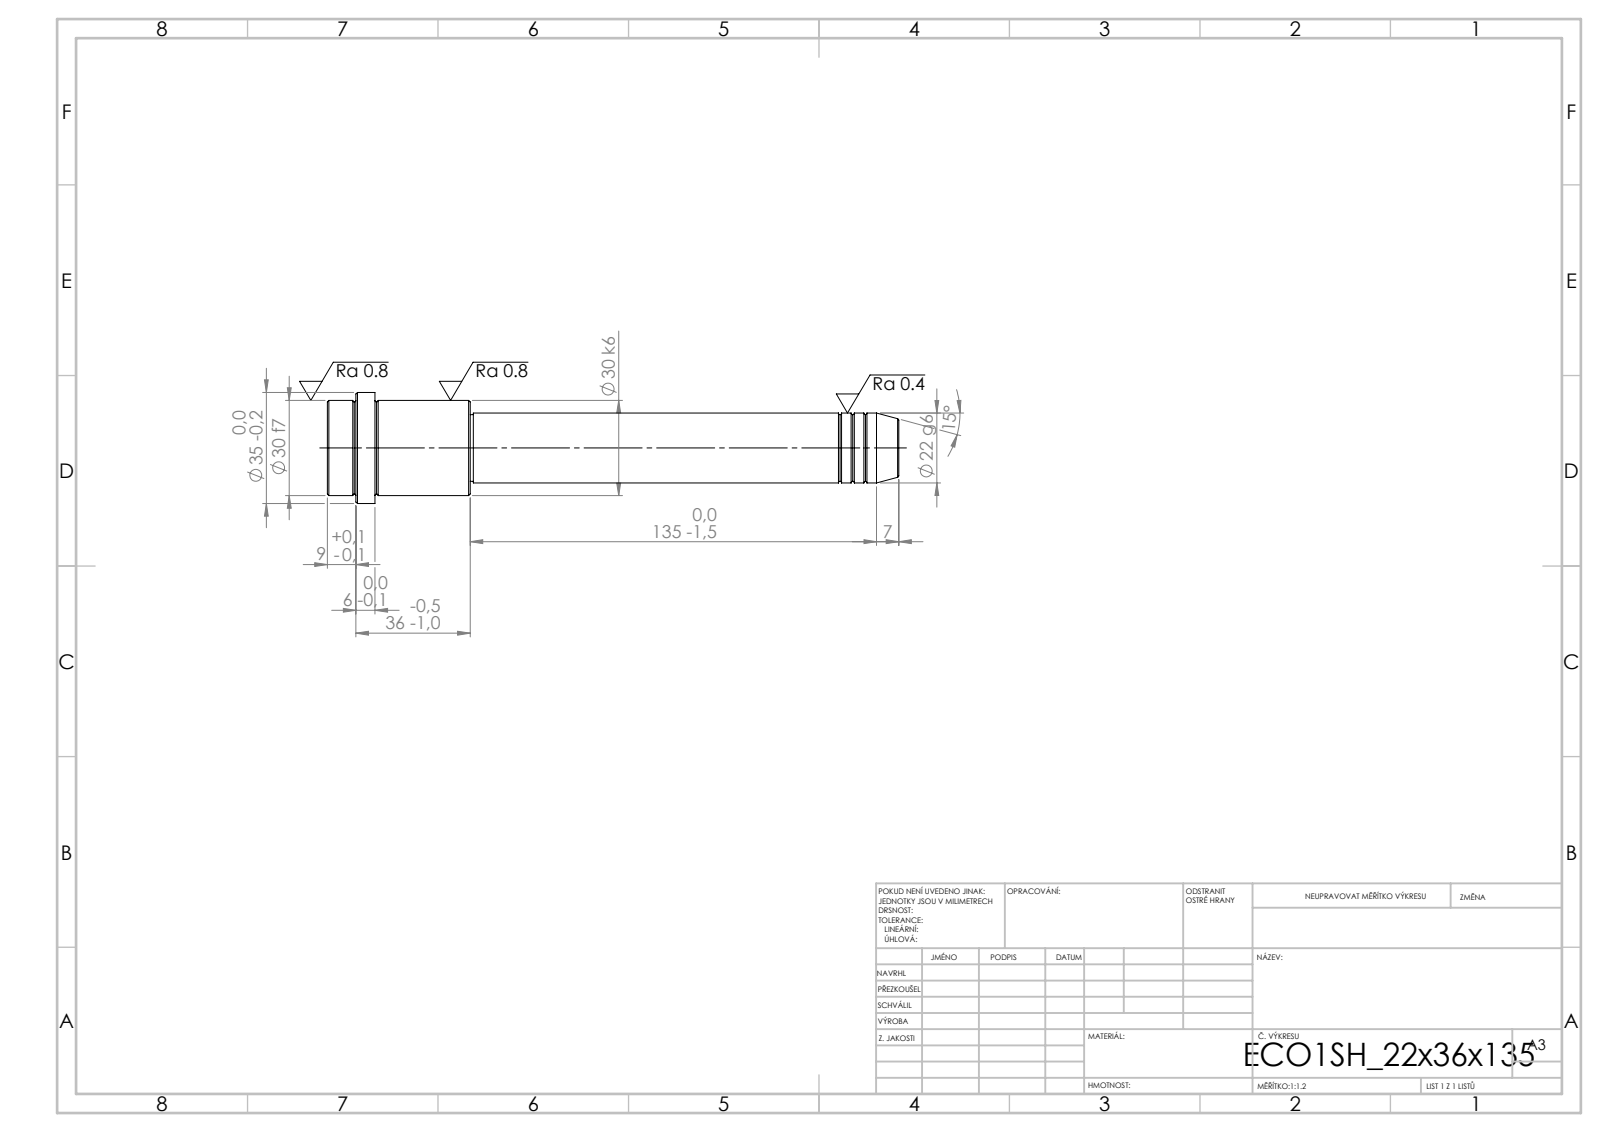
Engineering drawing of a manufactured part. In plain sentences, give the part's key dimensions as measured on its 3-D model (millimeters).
Its 3-D file was written by "SolidWorks 2019 (CONFIG_CONTROL_DESIGN)". It is 1 solid with 52 faces: 6 planar, 16 cylindrical and 30 other. Overall it measures 180 by 35 by 35 millimeters. Its volume is 84 005 cubic millimeters and its surface area 15 626 square millimeters. Round bosses or shafts: 1 of diameter 35, 1 of diameter 30, 1 of diameter 22, 1 of diameter 21. The main face-to-face distances are 45, 30, 15, 135, 165, 180, 171, 36, 6, 9.
